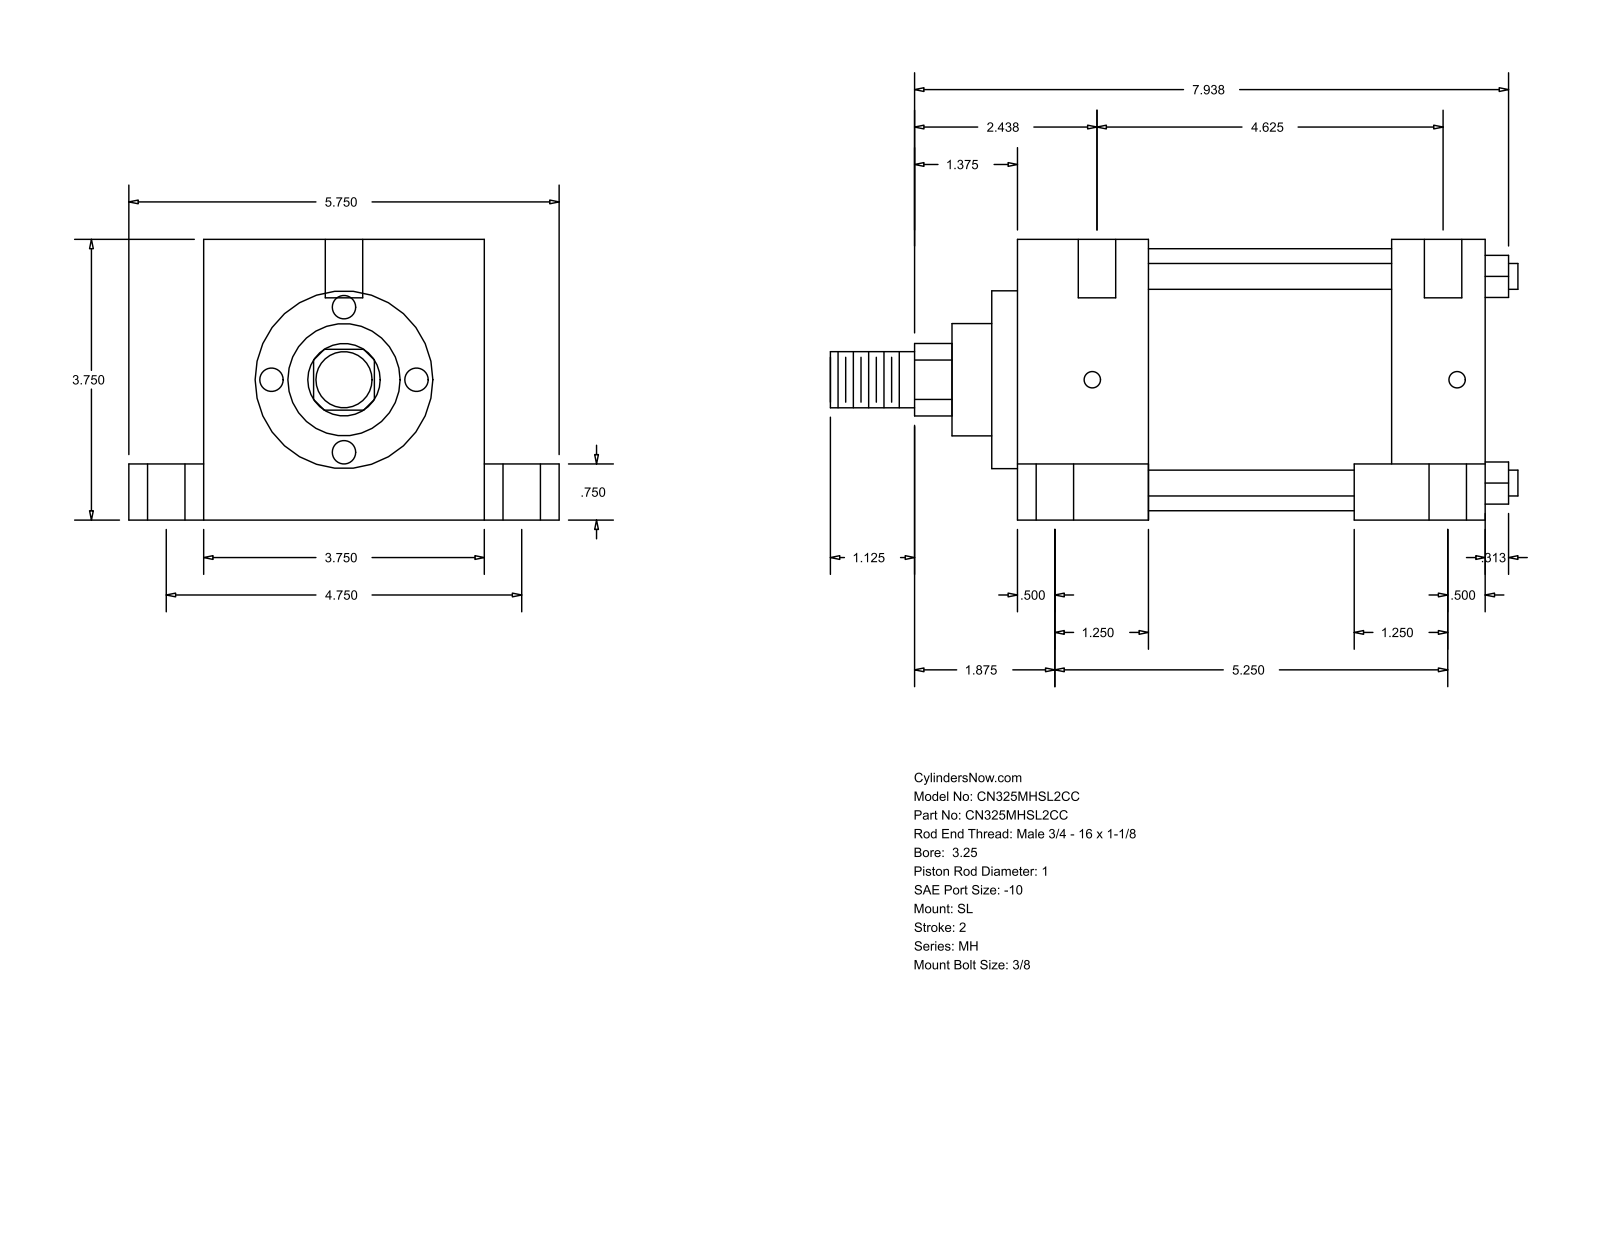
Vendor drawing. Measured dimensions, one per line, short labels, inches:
name: MH_SL__0325_1
written by: GSSL Pune (CONFIG_CONTROL_DESIGN)
unit: in
bodies: 0 solids, 110 faces (77 planar, 33 cylindrical, 0 other)
size: 9.187 × 5.75 × 3.75
holes: 6× ⌀0.5, 4× ⌀0.219, 4× ⌀0.75
bosses: 4× ⌀0.345, 1× ⌀3.5, 1× ⌀2.375, 1× ⌀1.5, 1× ⌀1, 1× ⌀0.75
rounds: 1× R0.484
face distances: 3.75, 6.25, 1.75, 4.5, 1, 4.75, 0.75, 3, 5, 3.25
hole spacings: 2.376, 2.378, 2.427, 2.441, 4.75, 4.875, 5.25, 5.255
